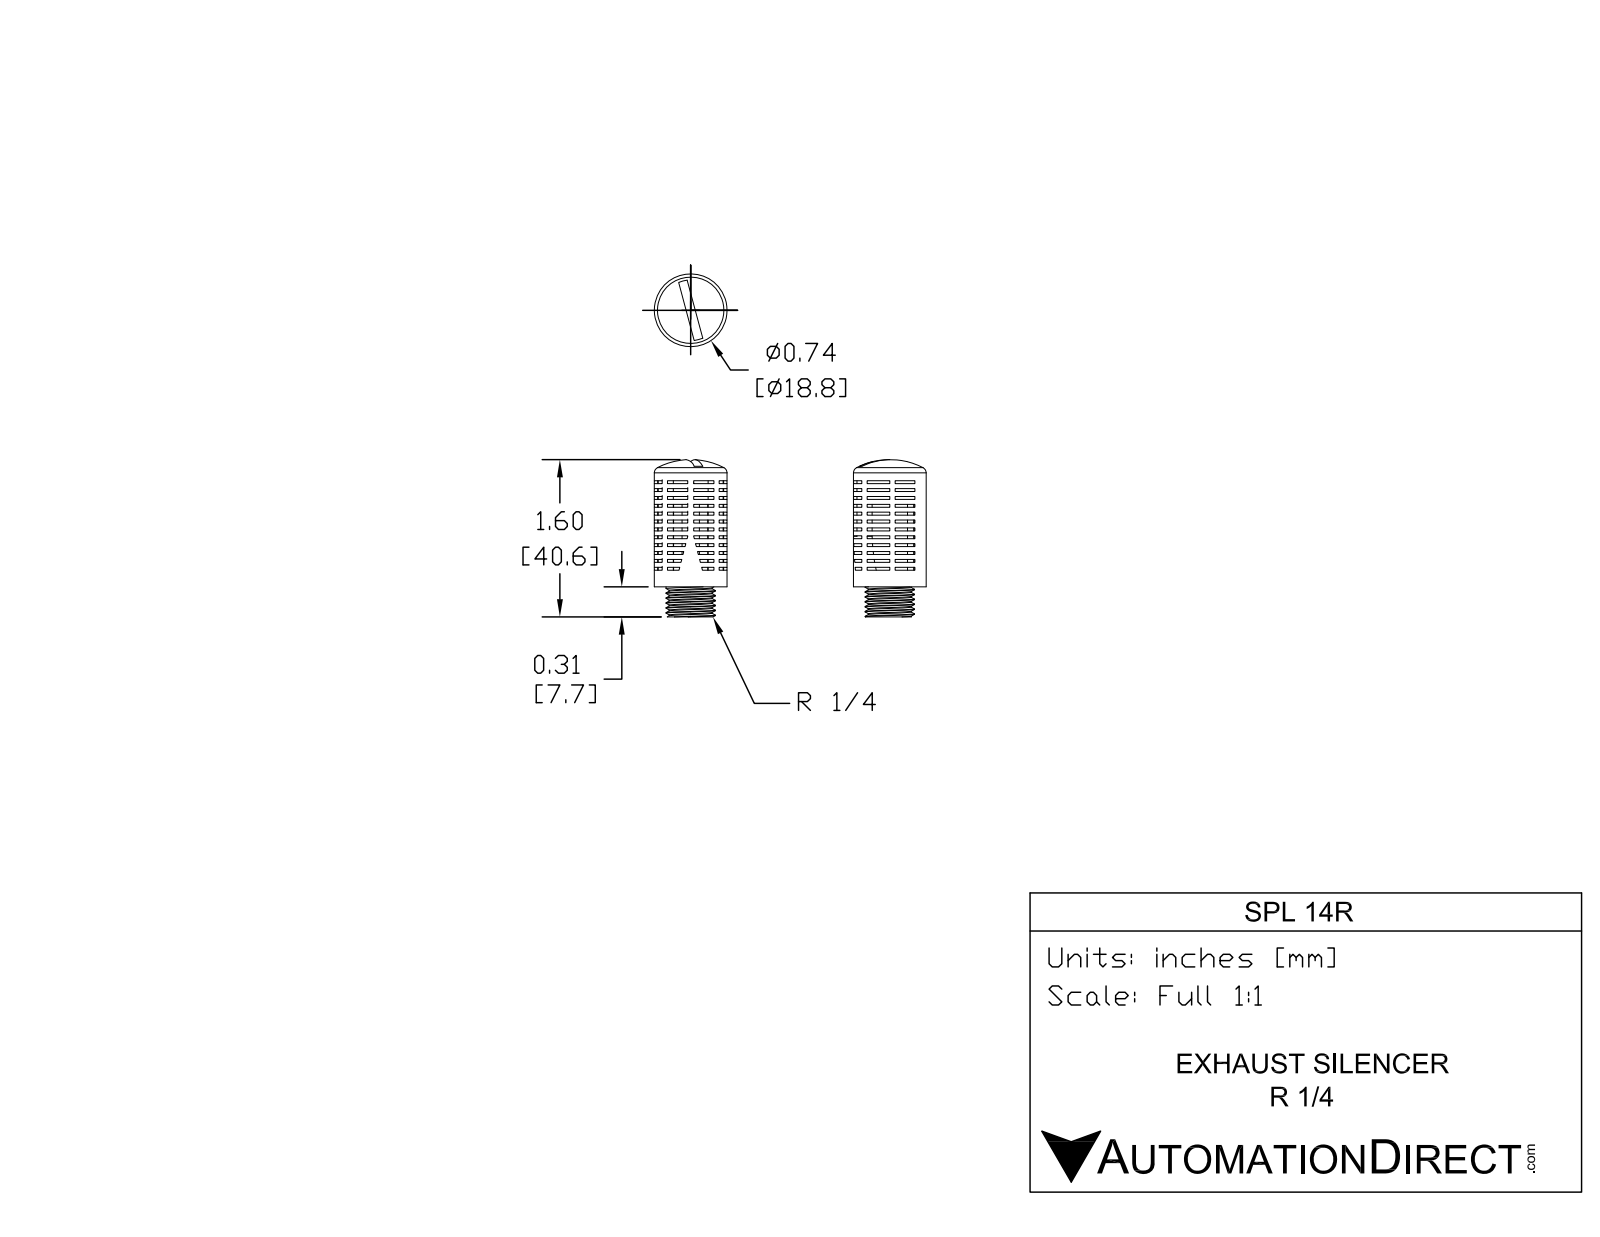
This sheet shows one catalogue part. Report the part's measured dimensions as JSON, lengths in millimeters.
{"part_name": "SPL-14R", "step_written_by": "SolidWorks 2015 (CONFIG_CONTROL_DESIGN)", "units": "millimeters", "bodies": {"solids": 1, "faces": 513, "planar": 483, "cylindrical": 22, "other": 8}, "overall_size": [42.6, 18.8, 18.8], "volume_mm3": 3650, "surface_area_mm2": 7787, "round_holes": [[9.3, 1], [17, 1]], "round_bosses_or_shafts": [[18.8, 1], [12.7, 1], [12.5, 1]], "face_to_face_distances": [2, 1.3, 0.8, 4.1, 4.1, 6.1, 8.1, 10.2, 2, 6.1]}
